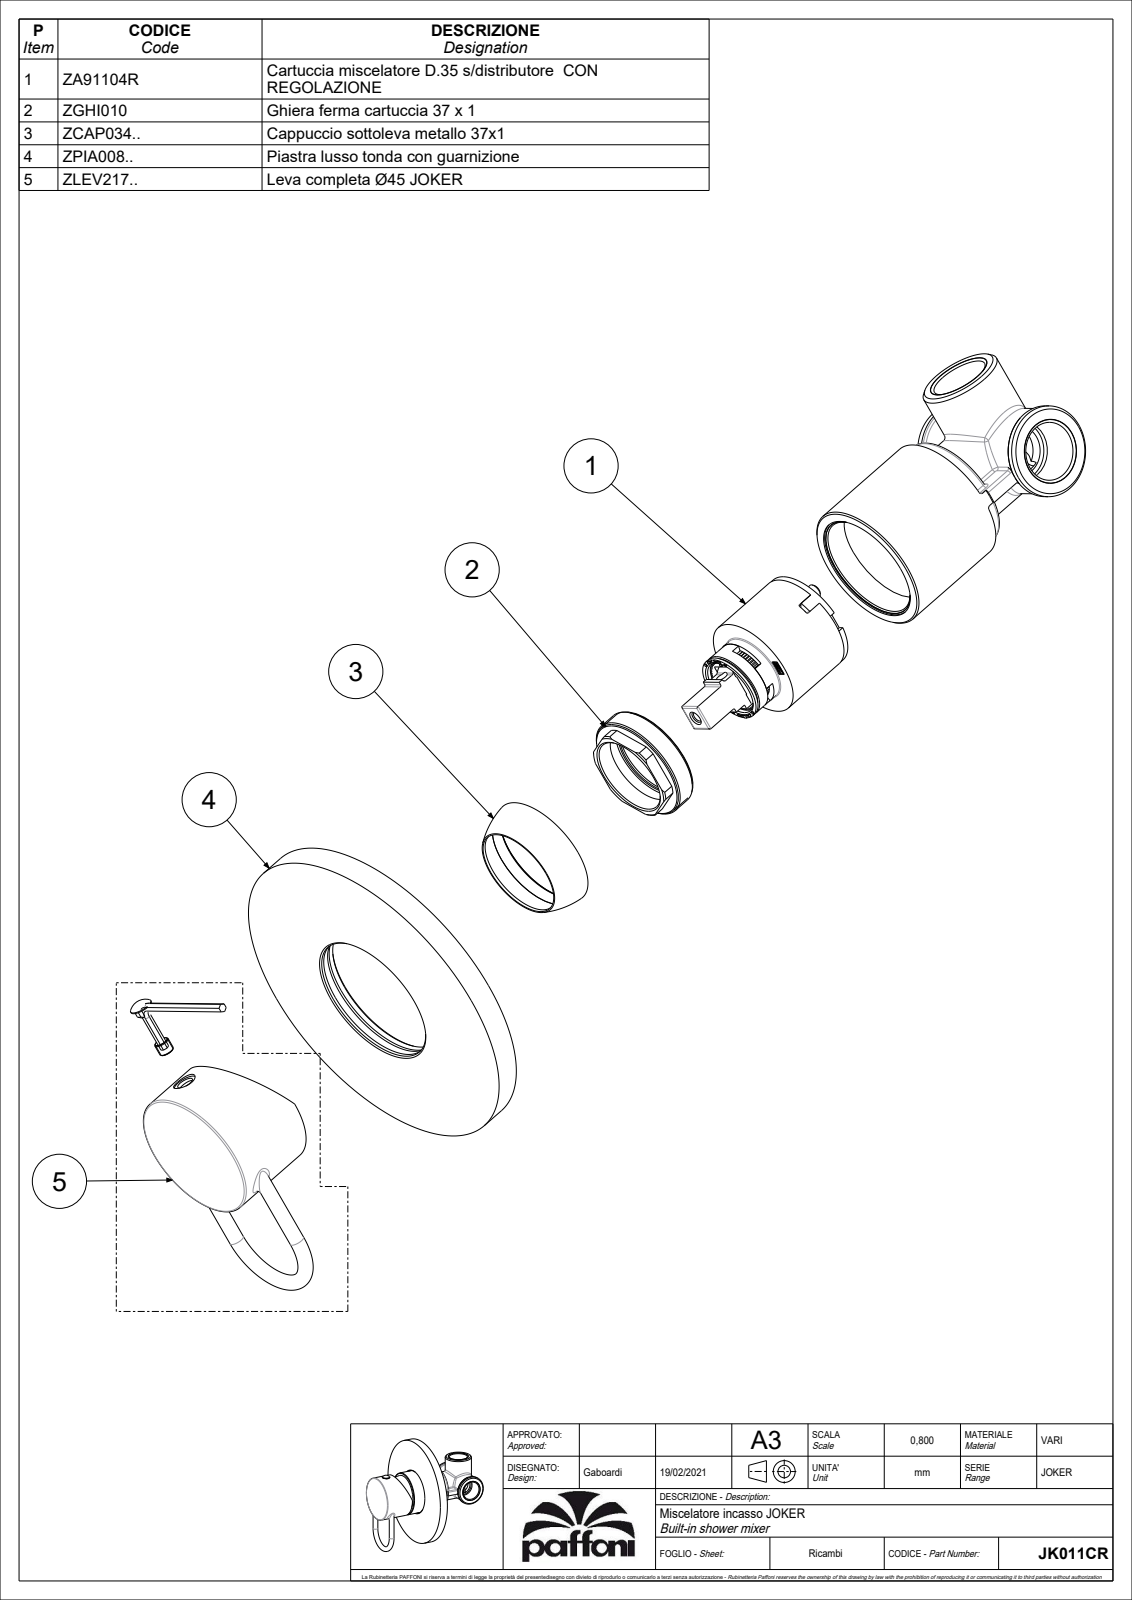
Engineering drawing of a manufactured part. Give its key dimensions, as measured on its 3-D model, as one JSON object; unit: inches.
{"part_name": "JK011CR", "step_written_by": "CREO PARAMETRIC BY PTC INC, 2020044 (CONFIG_CONTROL_DESIGN)", "units": "inches", "bodies": {"solids": 2, "faces": 861, "planar": 535, "cylindrical": 193, "other": 133}, "overall_size": [4.488, 4.331, 2.126], "volume_in3": 3.913, "surface_area_in2": 88.2, "round_holes": [[0.157, 2], [0.118, 1], [0.13, 1], [0.197, 1], [0.315, 1], [0.768, 1], [0.783, 1], [1.055, 1], [1.142, 1], [1.22, 1], [1.276, 1], [1.417, 1]], "round_bosses_or_shafts": [[0.197, 3], [4.331, 1], [2.15, 1], [1.772, 1], [1.764, 1], [1.378, 1], [0.925, 1], [0.921, 1]], "partial_cylinders_radius": [[0.006, 11], [0.02, 6], [0.012, 4], [0.039, 2], [0.061, 2], [0.276, 1], [0.366, 1], [0.427, 1]], "face_to_face_distances": [0.276, 1.953, 1.677, 0.059, 0.217, 0.354, 0.571, 0.63, 1.323, 1.894], "hole_center_spacings": [0.512]}
